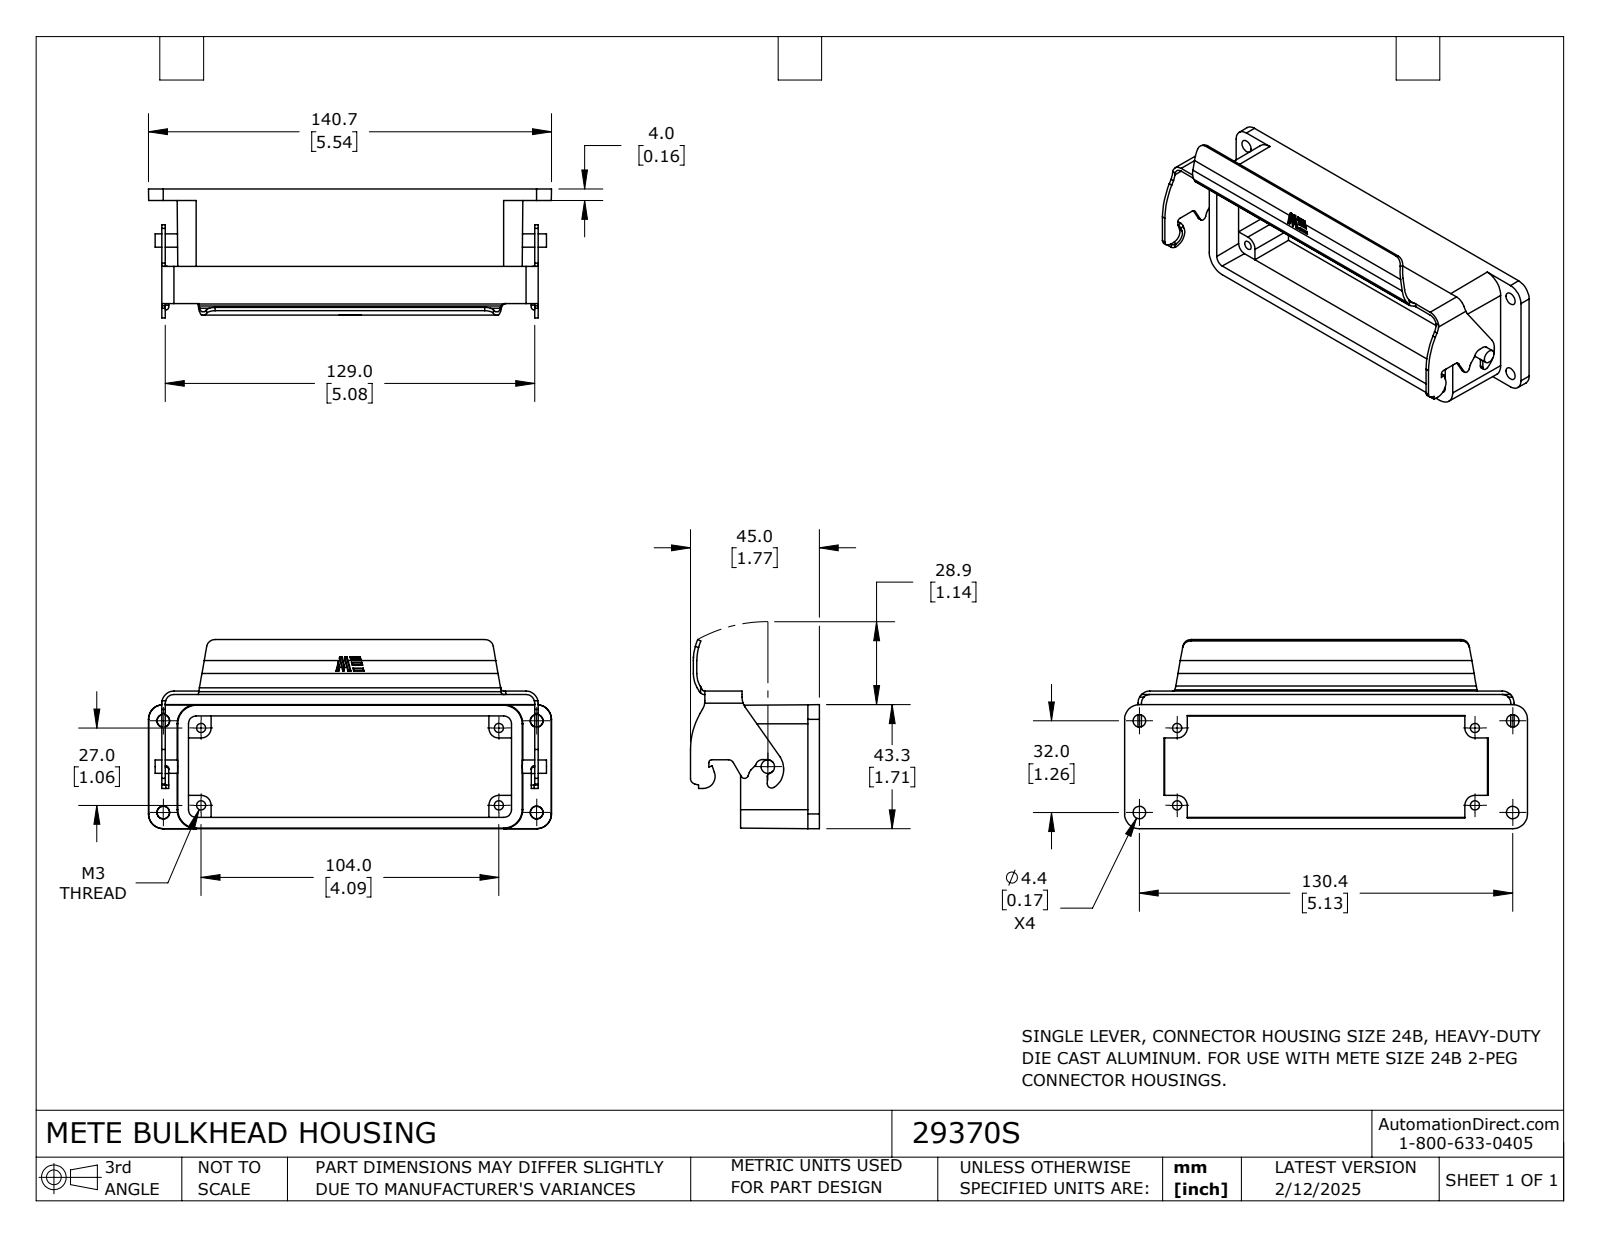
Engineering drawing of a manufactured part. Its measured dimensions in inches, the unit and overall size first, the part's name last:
Units: inches
Overall size (bounding box): 5.541 × 2.601 × 1.772
Round holes (diameter × count): ⌀0.126 ×4
Round bosses / shafts (diameter × count): ⌀0.185 ×1
Partial cylindrical surfaces — rounded edges, fillets, slot ends (radius × count): R0.008 ×17, R0.039 ×6, R0.118 ×5, R0.138 ×4, R0.079 ×3, R0.098 ×3, R0.165 ×3, R0.059 ×2
Main face-to-face distances: 0.047, 0.335, 1.744, 0.287, 1.697, 1.409, 1.083, 5.126, 0.311, 0.157
Hole centre spacings: 1.063, 4.094, 4.23
Volume: 2.679 in³ · Surface area: 51.27 in²
Bodies: 1 solid, 213 faces (94 planar, 95 cylindrical, 24 other)
Part name (STEP PRODUCT): 29370S
STEP written by: SolidWorks 2024 (CONFIG_CONTROL_DESIGN)
